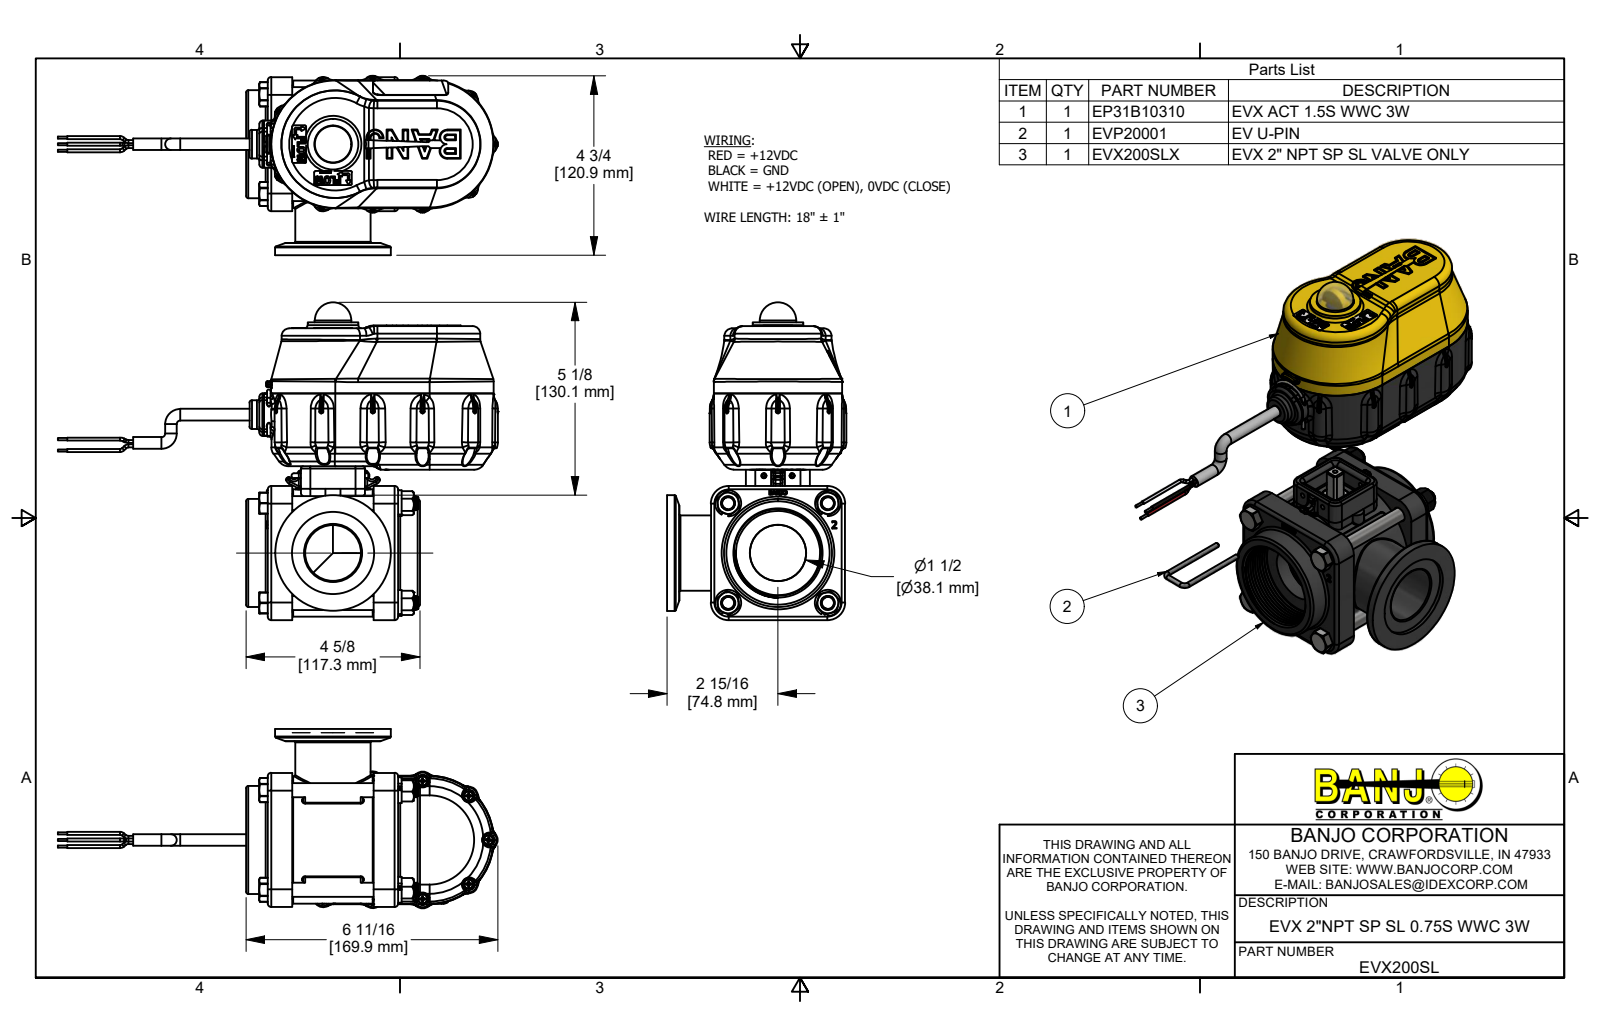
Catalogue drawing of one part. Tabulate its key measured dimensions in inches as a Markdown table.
| quantity | value |
| --- | --- |
| part name | EVX200SL; EP31B10310; B61905PPHS; B632038PM (+8 more) |
| STEP written by | Autodesk Inventor 2019 (AUTOMOTIVE_DESIGN) |
| units | inches |
| bodies | 98 solids, 11837 faces (3268 planar, 3356 cylindrical, 5213 other) |
| overall size | 11.685 × 8.437 × 4.76 |
| volume | 63.99 in³ |
| surface area | 679 in² |
| round holes (diameter × count) | 0.095 × 11, 0.15 × 11, 0.08 × 7, 0.107 × 4, 0.126 × 4, 0.136 × 4, 0.148 × 4, 0.15 × 4, 0.17 × 4, 0.307 × 4, 0.385 × 4, 0.406 × 4 |
| round bosses / shafts (diameter × count) | 0.324 × 60, 0.25 × 17, 0.08 × 15, 0.14 × 11, 0.108 × 11, 0.085 × 11, 0.058 × 6, 0.375 × 5 |
| partial cylindrical surfaces (radius × count) | 0.013 × 180, 0.04 × 145, 0.01 × 84, 0.02 × 80, 0.005 × 53, 0.03 × 30, 0.06 × 28, 0.08 × 28 |
| main face-to-face distances | 0.1, 2.565, 0.65, 2.808, 0.211, 0.06, 0.151, 0.125, 1.896, 1.836 |
| hole center spacings | 1.872, 2.648, 2.656, 1.662, 1.774, 2.088, 2.69, 2.73 |
